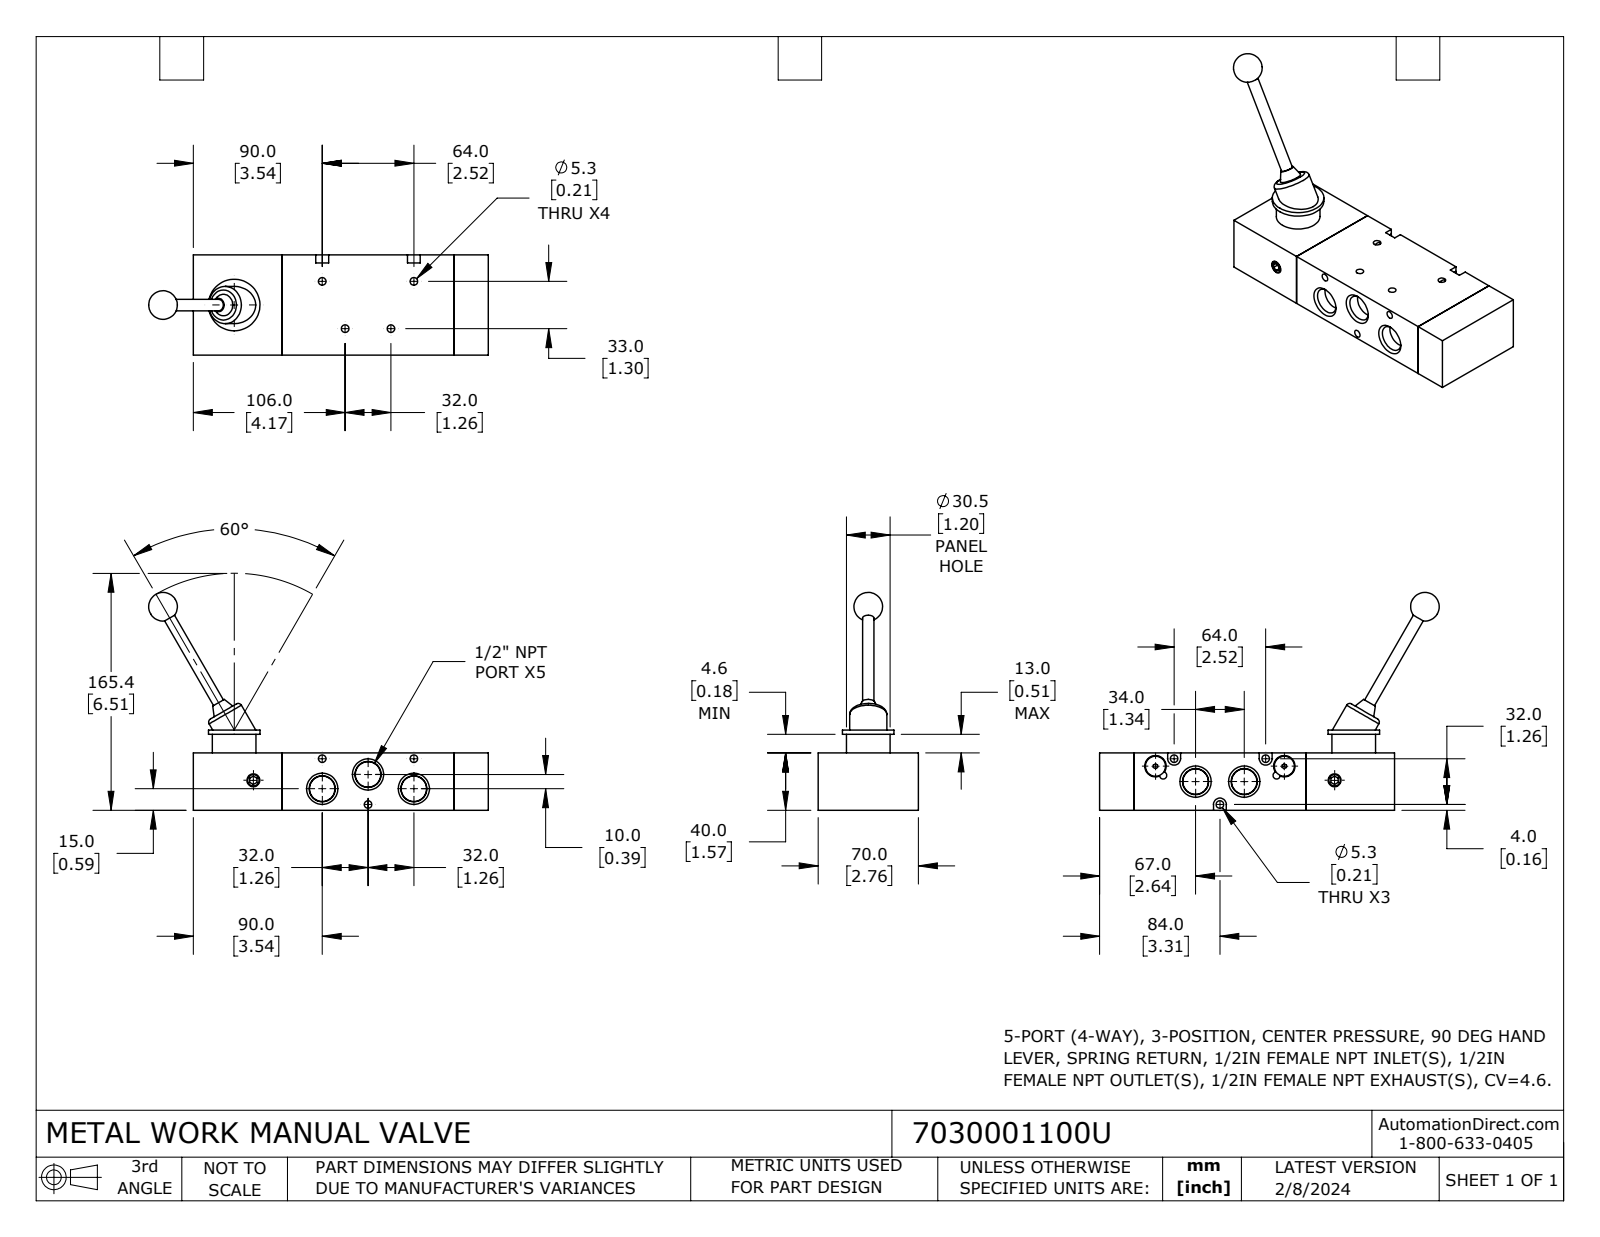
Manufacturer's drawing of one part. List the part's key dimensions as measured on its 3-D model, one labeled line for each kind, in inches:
Part name (STEP PRODUCT): 7030001100U
STEP written by: SolidWorks 2023 (CONFIG_CONTROL_DESIGN)
Units: inches
Bodies: 3 solids, 155 faces (72 planar, 57 cylindrical, 26 other)
Overall size (bounding box): 9.339 × 5.988 × 2.756
Volume: 35.65 in³ · Surface area: 120.8 in²
Round holes (diameter × count): ⌀0.209 ×7, ⌀0.587 ×2, ⌀0.354 ×1
Round bosses / shafts (diameter × count): ⌀0.551 ×2, ⌀1.417 ×1, ⌀1.201 ×1, ⌀1.024 ×1, ⌀0.315 ×1, ⌀0.313 ×1
Partial cylindrical surfaces — rounded edges, fillets, slot ends (radius × count): R0.177 ×3, R0.098 ×2
Main face-to-face distances: 1.575, 2.756, 4.724, 0.945, 5.669, 8.11, 7.165, 2.441, 0.354, 2.402
Hole centre spacings: 0.552, 1.444, 1.781, 2.061, 2.293, 2.52, 3.039, 1.26
